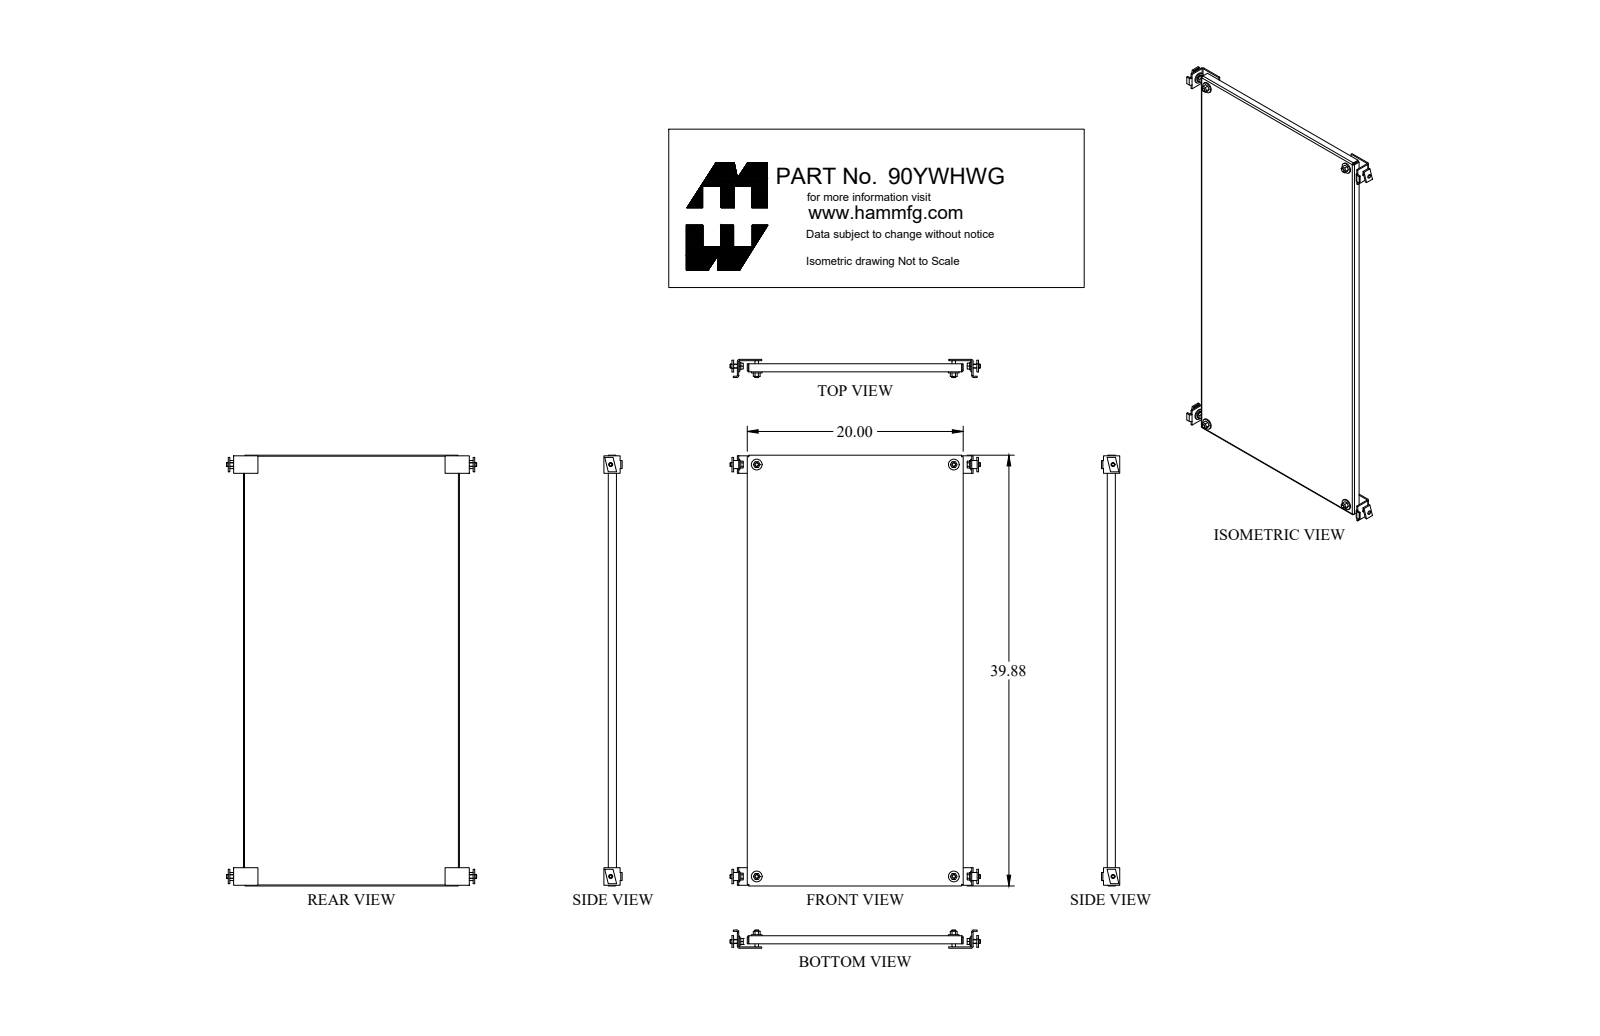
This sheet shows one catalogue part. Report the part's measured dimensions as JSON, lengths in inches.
{"part_name": "90YWHWG_Default", "step_written_by": "SolidWorks 2018 (CONFIG_CONTROL_DESIGN)", "units": "inches", "bodies": {"solids": 9, "faces": 190, "planar": 94, "cylindrical": 64, "other": 32}, "overall_size": [39.875, 22.582, 1.687], "volume_in3": 86.28, "surface_area_in2": 1815, "round_holes": [[0.563, 4], [0.437, 2]], "round_bosses_or_shafts": [[0.65, 4], [0.375, 4], [0.33, 4]], "partial_cylinders_radius": [[0.048, 4], [0.06, 4], [0.143, 4], [0.185, 4]], "face_to_face_distances": [0.095, 19.905, 19.81, 20, 39.78, 0.125, 1.032, 0.937, 1.157, 1.062], "hole_center_spacings": [18.25, 38.125, 42.268, 38.13]}
